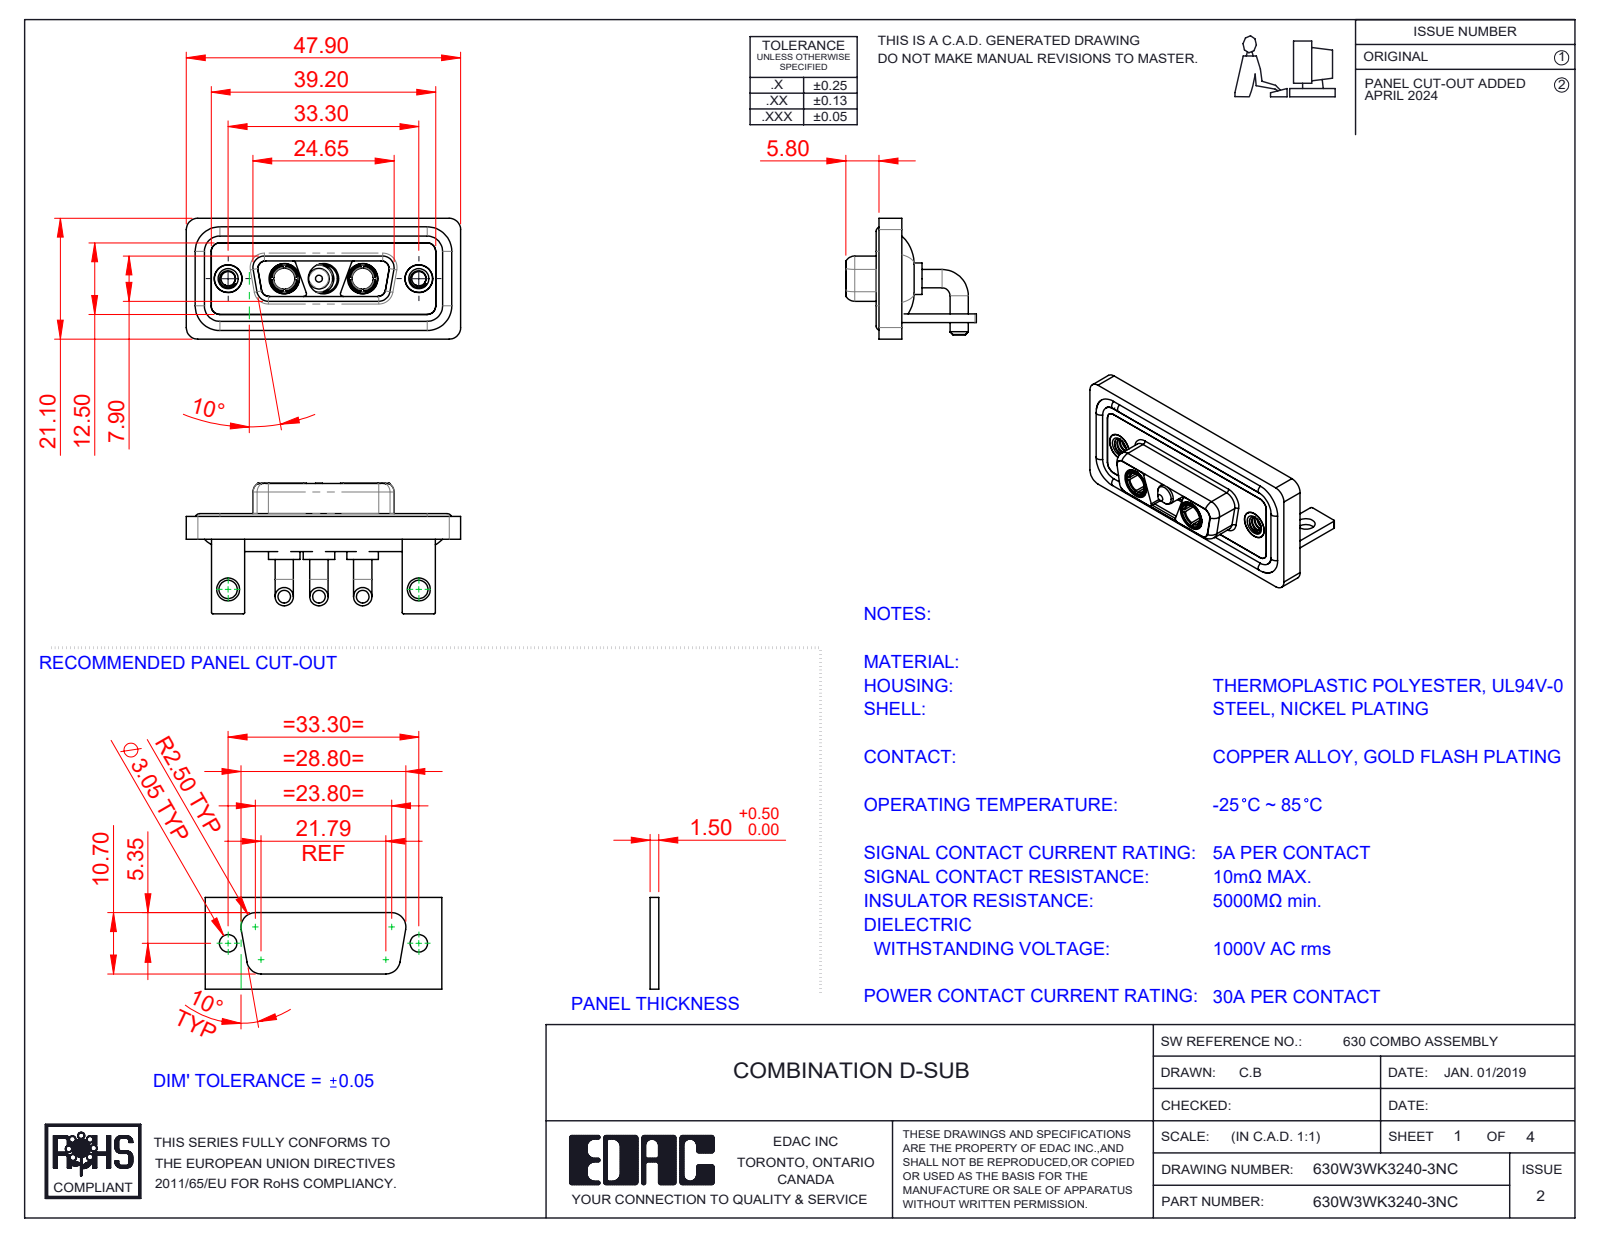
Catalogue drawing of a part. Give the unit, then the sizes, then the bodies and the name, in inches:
Units: inches
Overall size (bounding box): 1.886 × 0.898 × 0.831
Round holes (diameter × count): ⌀0.191 ×5, ⌀0.209 ×3, ⌀0.098 ×2, ⌀0.126 ×2, ⌀0.146 ×2, ⌀0.157 ×2, ⌀0.159 ×2, ⌀0.197 ×2
Round bosses / shafts (diameter × count): ⌀0.126 ×6, ⌀0.063 ×4, ⌀0.217 ×3, ⌀0.205 ×3, ⌀0.187 ×3, ⌀0.148 ×3, ⌀0.195 ×2, ⌀0.195 ×2
Partial cylindrical surfaces — rounded edges, fillets, slot ends (radius × count): R0.079 ×21, R0.059 ×18, R0.01 ×16, R0.053 ×12, R0.02 ×9, R0.063 ×8, R0.024 ×4, R0.026 ×4
Main face-to-face distances: 0.016, 0.114, 0.059, 0.146, 0.071, 0.043, 0.161, 0.063, 0.098, 0.055
Hole centre spacings: 0.27, 0.386, 0.656, 0.925, 1.311, 0.539
Volume: 0.395 in³ · Surface area: 16.32 in²
Bodies: 15 solids, 637 faces (198 planar, 286 cylindrical, 153 other)
Part name (STEP PRODUCT): 630Combo Shell Front_15 Contacts; 630Combo Shell Rear_15 Contacts; 630Combo Waterproof Housing_15 Contacts; 630Combo Stabilizer Bracket_50 Contacts (+5 more)
STEP written by: SolidWorks 2023 (CONFIG_CONTROL_DESIGN)
